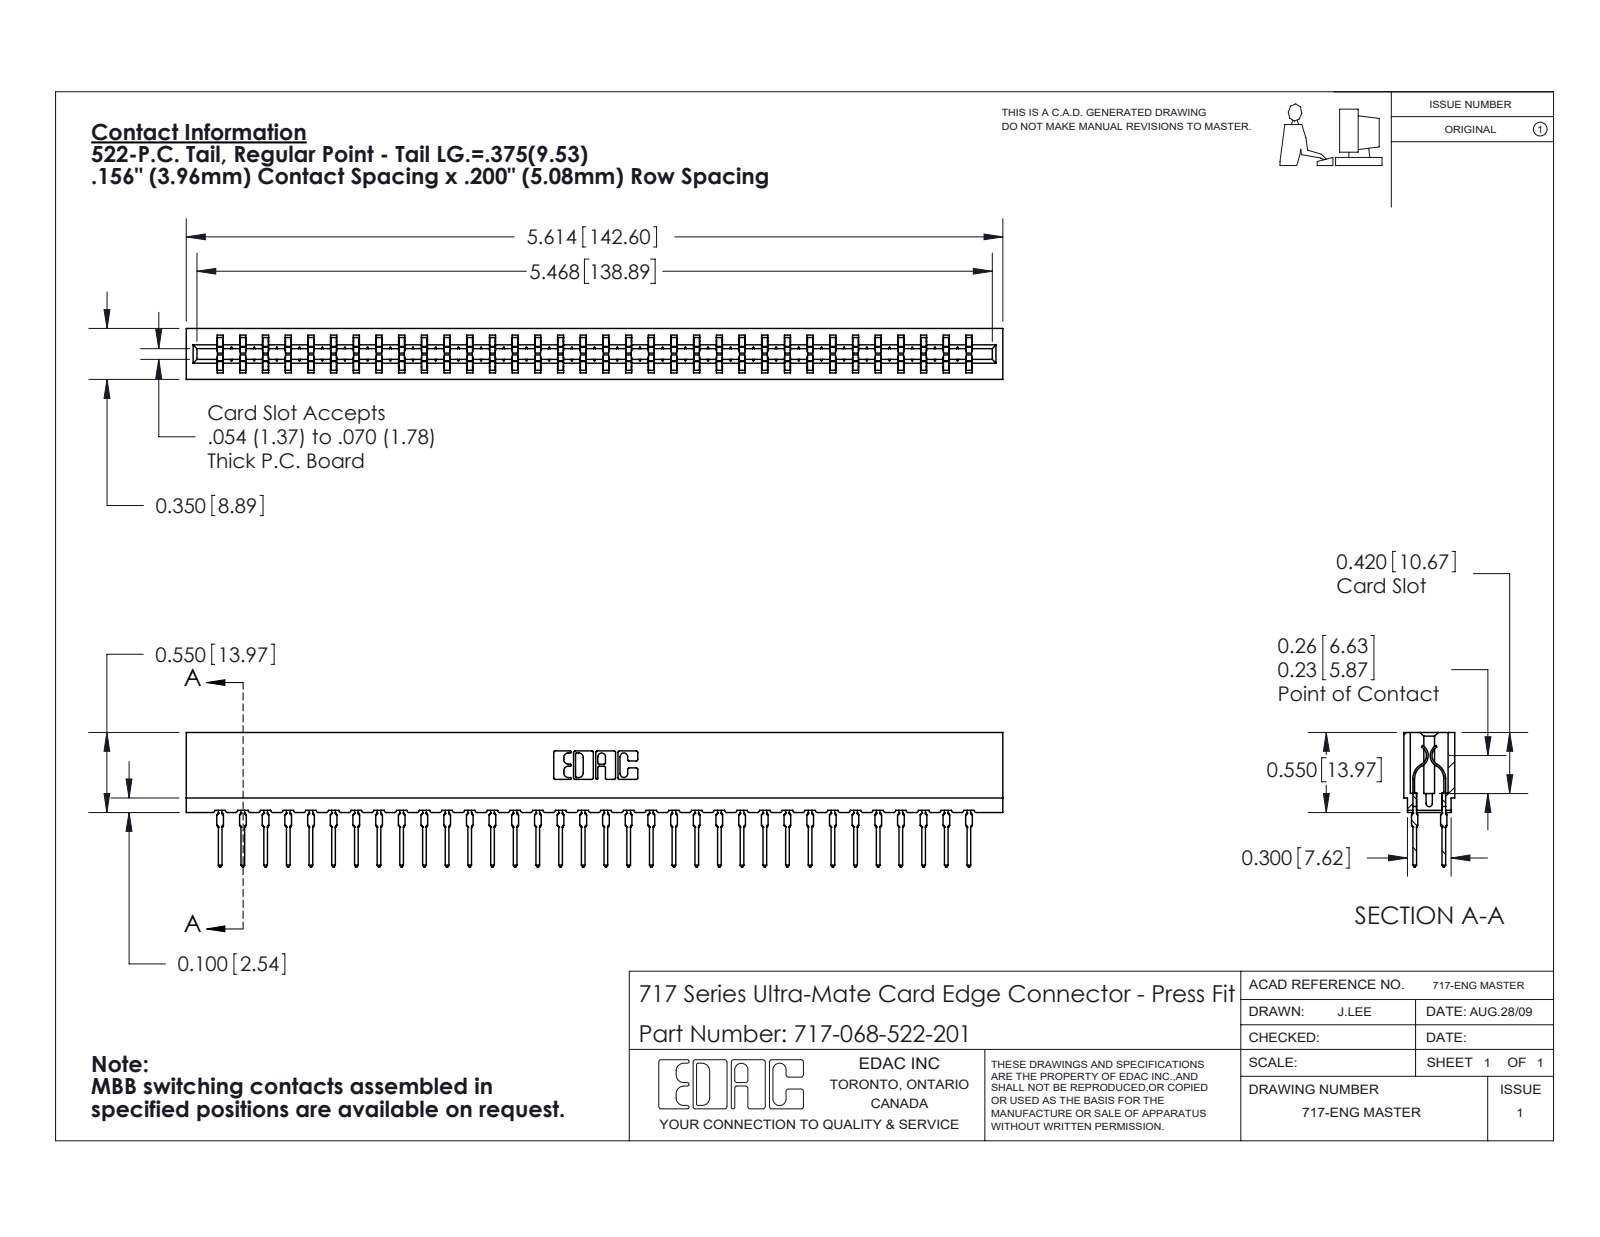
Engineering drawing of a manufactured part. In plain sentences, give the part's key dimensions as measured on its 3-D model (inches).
The part is named "717-068-522-201; 745-292-001_522; 717 Part_Insulator Option - 06". Its 3-D file was written by "SolidWorks 2020 (CONFIG_CONTROL_DESIGN)". It is 69 solids with 6214 faces: 3216 planar, 1230 cylindrical and 1768 other. Overall it measures 5.614 by 0.924 by 0.35 inches. Its volume is 0.76 cubic inches and its surface area 29.8 square inches. Partial cylindrical surfaces (rounded edges, fillets, slot ends): 136 of radius 0.021, 68 of radius 0.015, 22 of radius 0.01, 8 of radius 0.005, 8 of radius 0.011, 6 of radius 0.007, 6 of radius 0.031, 3 of radius 0.026. The main face-to-face distances are 0.212, 0.138, 0.35, 0.063, 0.287, 0.076, 0.149, 0.074, 0.156, 0.045.
